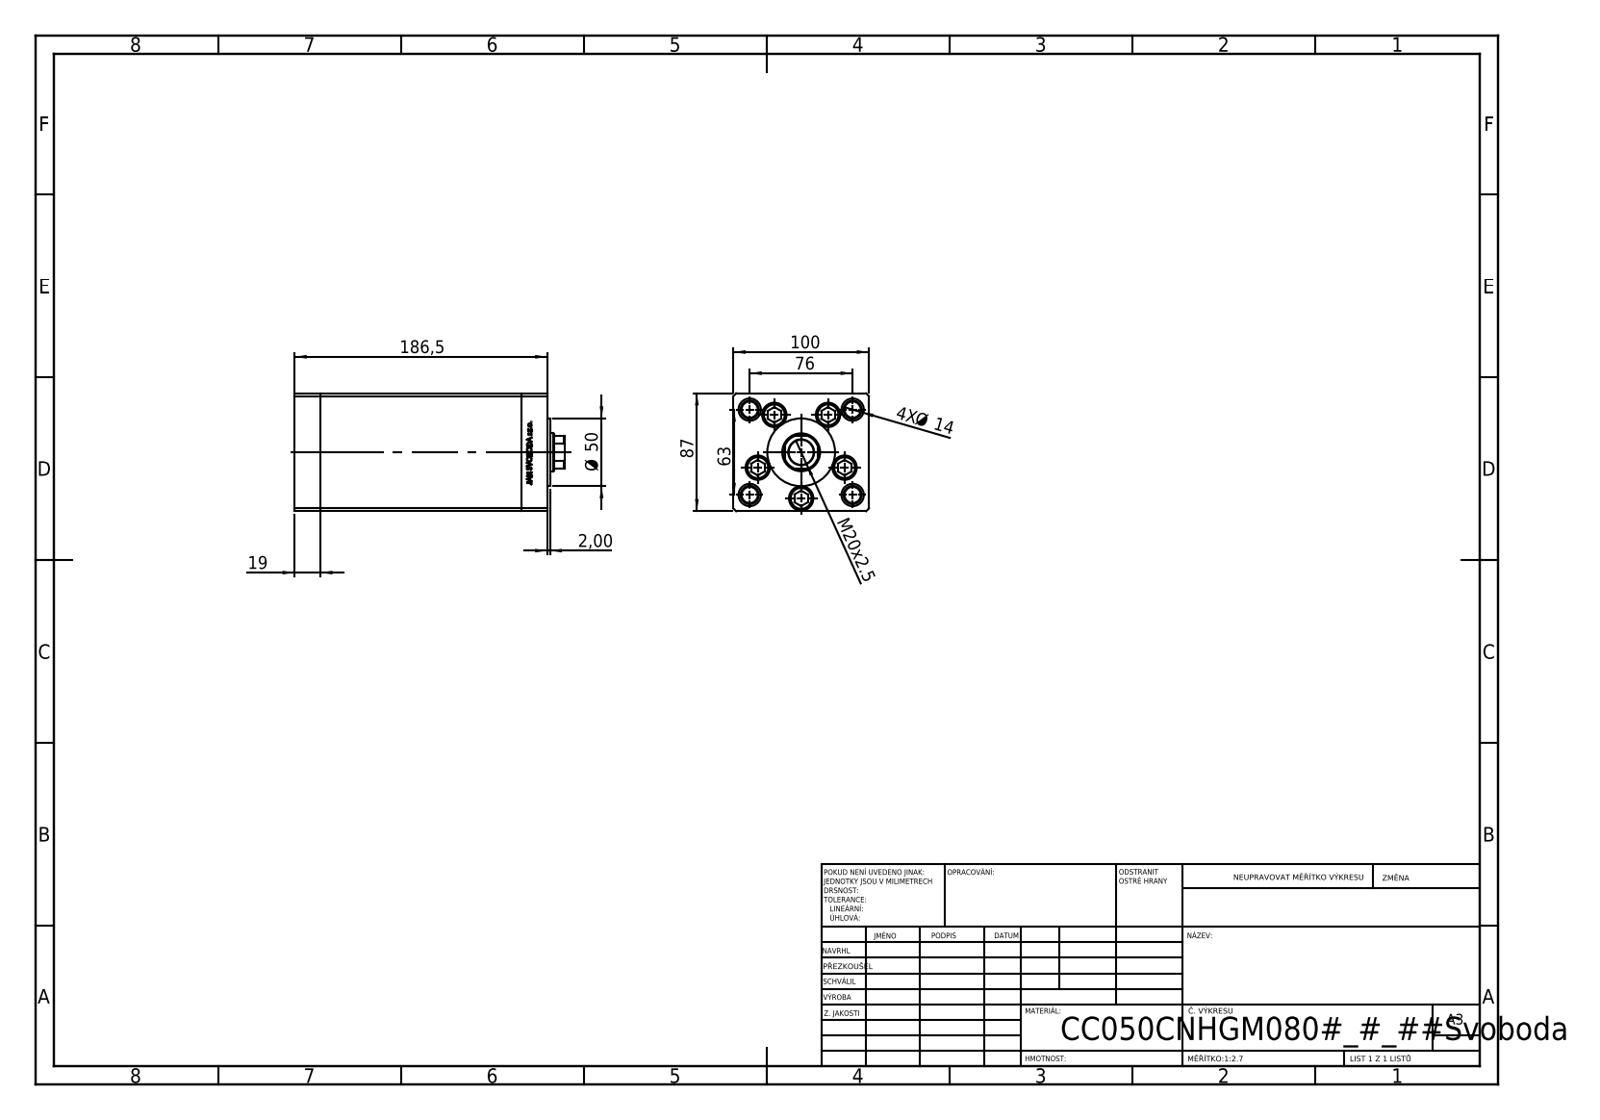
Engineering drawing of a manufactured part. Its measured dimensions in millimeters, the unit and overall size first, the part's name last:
Units: millimetres
Overall size (bounding box): 199.5 × 100 × 87
Round holes (diameter × count): ⌀13.5 ×9, ⌀18 ×5, ⌀2 ×4, ⌀12 ×4, ⌀13.16 ×4, ⌀16.5 ×4, ⌀17 ×1, ⌀18.5 ×1, ⌀28 ×1
Round bosses / shafts (diameter × count): ⌀8 ×5, ⌀17 ×4, ⌀50 ×1
Partial cylindrical surfaces — rounded edges, fillets, slot ends (radius × count): R0.93 ×2, R13.5 ×1
Main face-to-face distances: 100, 87, 19, 148.5, 167.5, 34.25, 186.5, 152.25, 133.25, 15.25
Hole centre spacings: 34, 49.36, 18.59, 21.03, 38.08, 39.27, 40.83, 43.24
Volume: 1 328 000 mm³ · Surface area: 230 838 mm²
Bodies: 13 solids, 1182 faces (544 planar, 176 cylindrical, 462 other)
Part name (STEP PRODUCT): V220C BACK_C; V220C_C MIDDLE; V220C_VC_C; ALLEN BOLT (+1 more)
STEP written by: SolidWorks 2019 (CONFIG_CONTROL_DESIGN)
